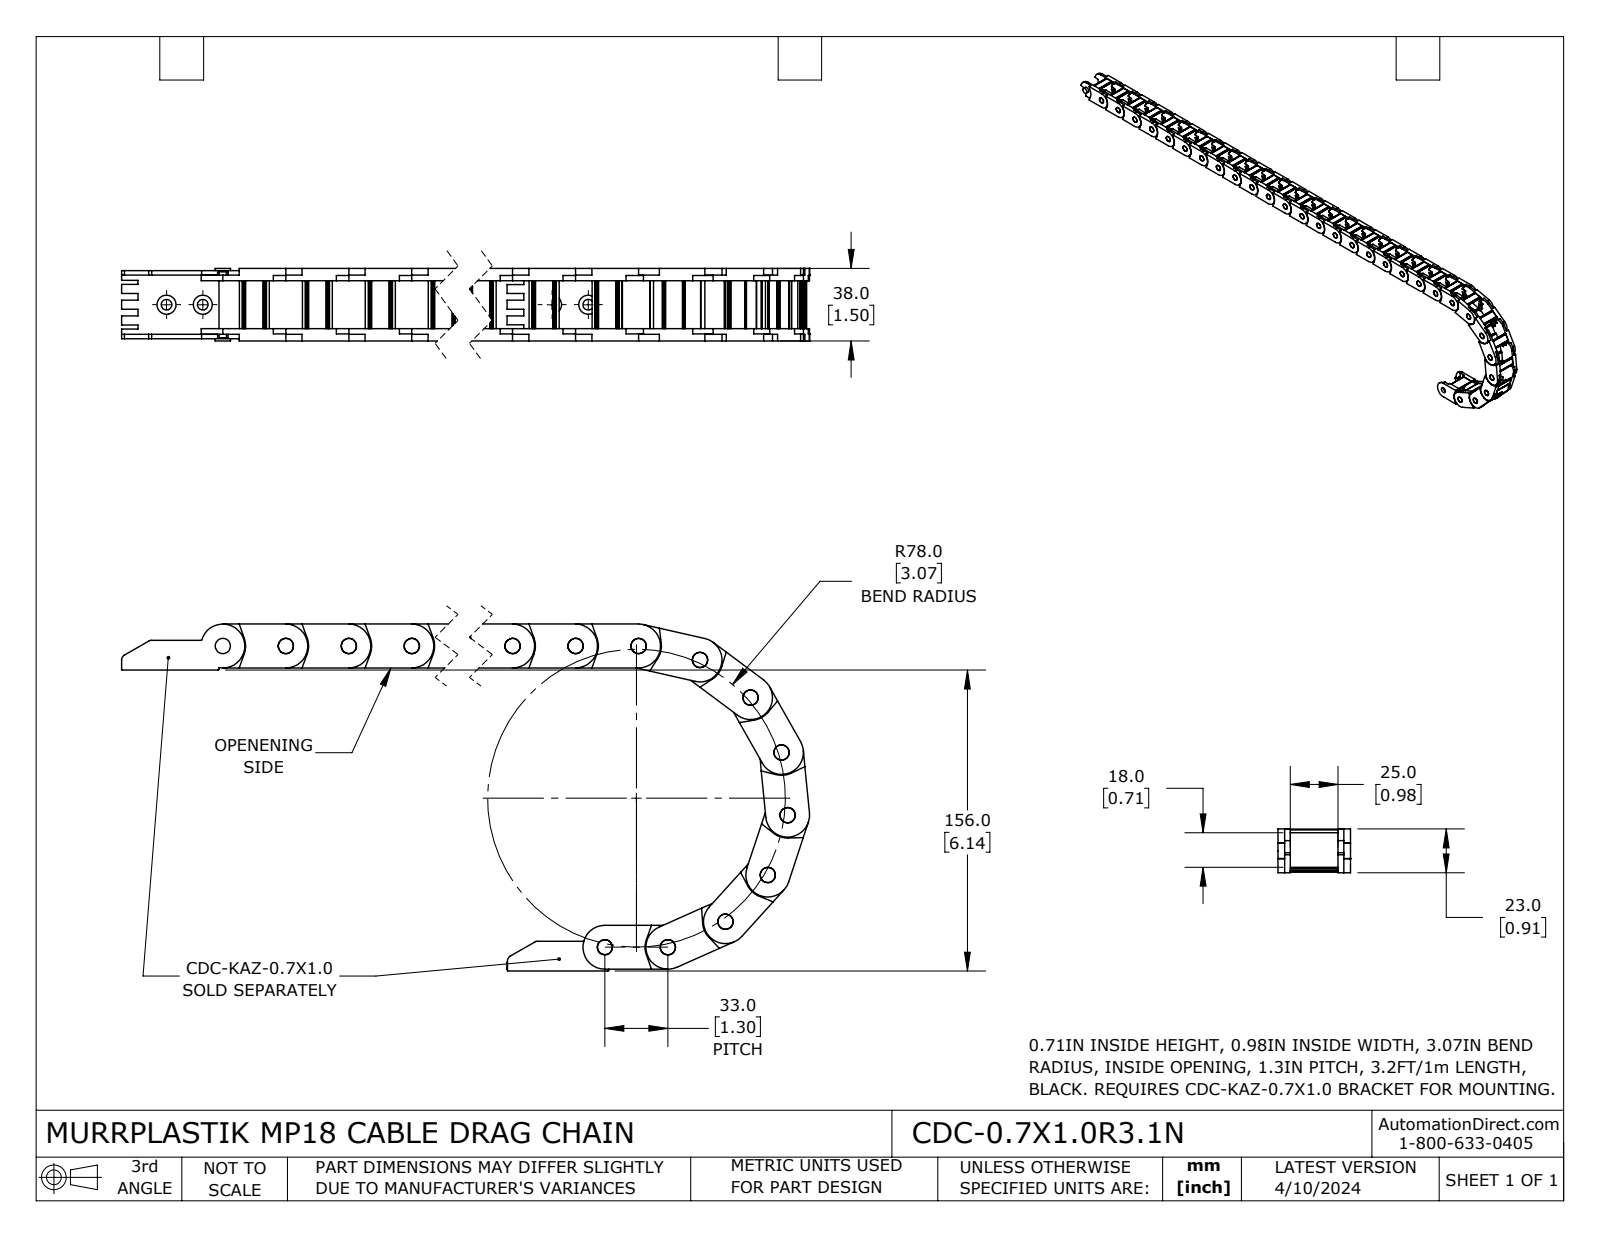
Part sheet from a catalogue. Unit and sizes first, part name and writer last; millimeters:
Units: millimetres
Overall size (bounding box): 826.89 × 180.72 × 38
Round holes (diameter × count): ⌀8 ×30
Round bosses / shafts (diameter × count): ⌀8 ×1
Partial cylindrical surfaces — rounded edges, fillets, slot ends (radius × count): R0.5 ×120, R1.5 ×120, R0.2 ×60, R0.3 ×60, R11.5 ×31, R11.95 ×31, R5 ×30, R5.45 ×30
Main face-to-face distances: 6.5, 31.5, 38, 3.5, 34.5, 3, 28, 25, 3.7, 34.3
Hole centre spacings: 33, 66, 99, 132, 165, 198, 231, 264
Volume: 307 300 mm³ · Surface area: 223 840 mm²
Bodies: 30 solids, 2550 faces (1290 planar, 1260 cylindrical, 0 other)
Part name (STEP PRODUCT): CDC-0.7X1.0R3.1N
STEP written by: SolidWorks 2023 (CONFIG_CONTROL_DESIGN)
